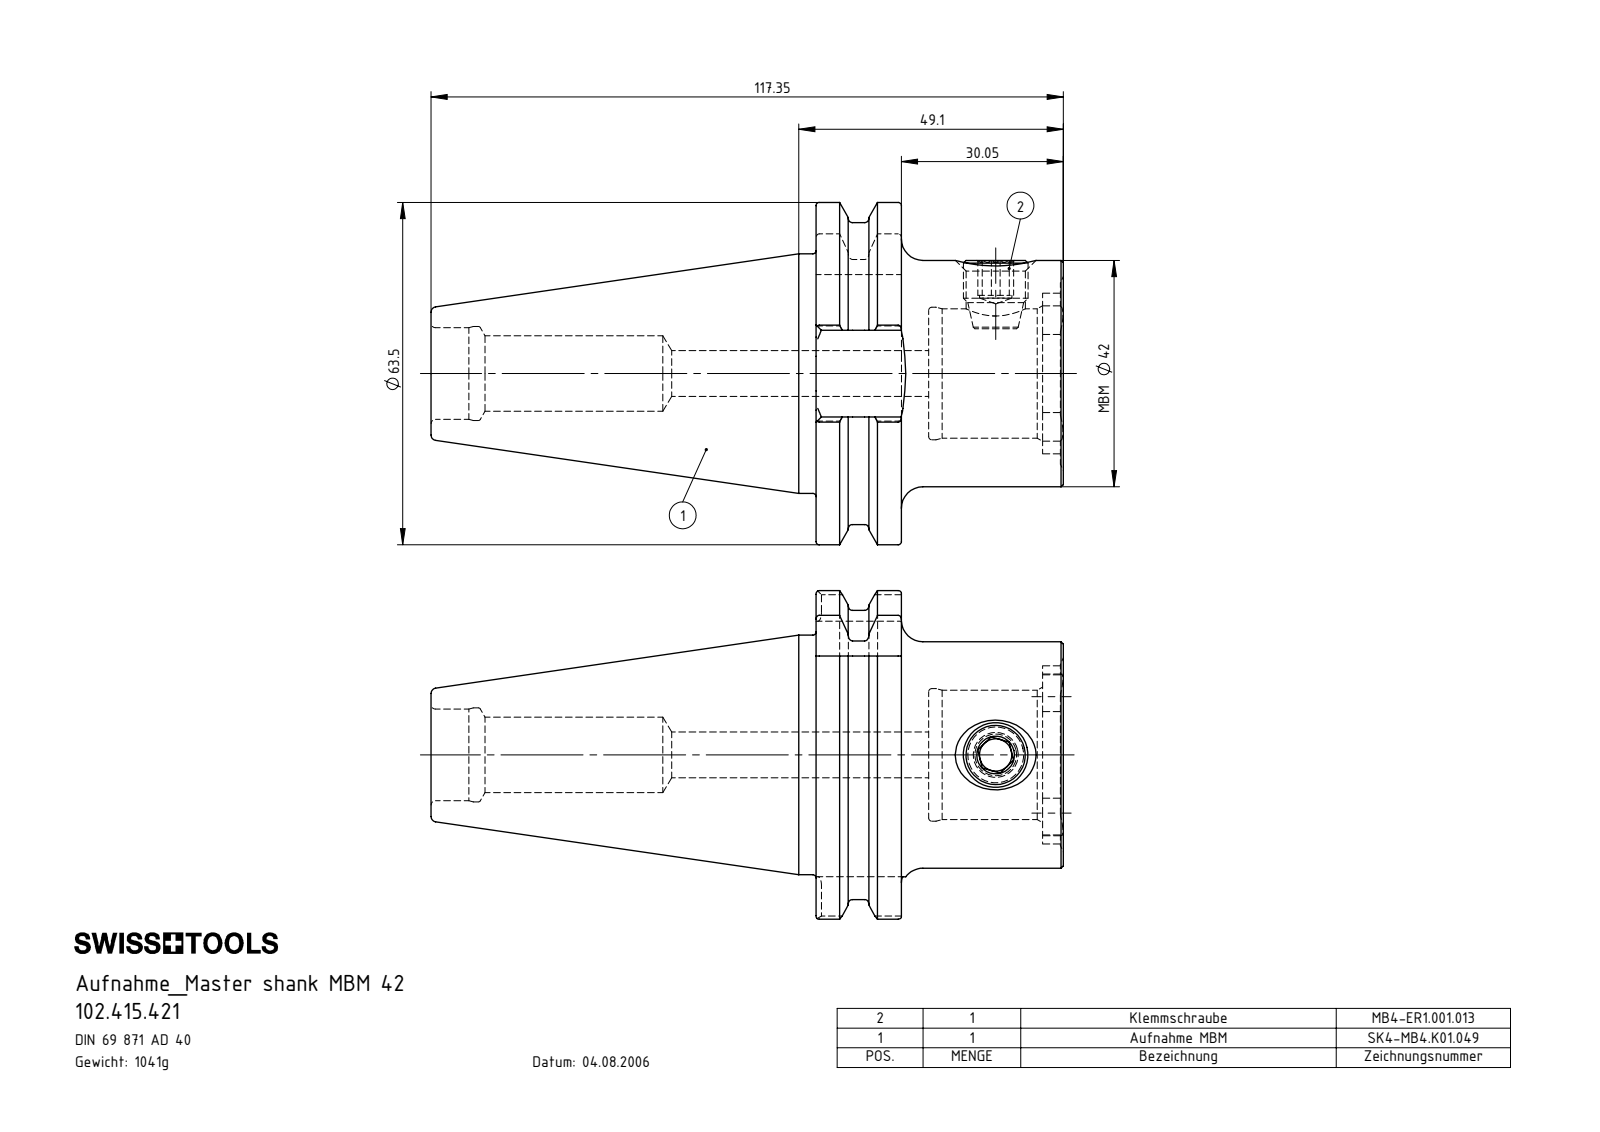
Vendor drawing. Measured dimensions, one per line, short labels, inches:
name: SK4-MB4.K01.049_C; MB4-ER1.001.013_A; 102.415.421
written by: SolidWorks 2017 (CONFIG_CONTROL_DESIGN)
unit: in
bodies: 2 solids, 170 faces (56 planar, 50 cylindrical, 64 other)
size: 4.62 × 2.5 × 2.399
volume: 8.091 in³; area: 40.51 in²
holes: 1× ⌀0.236, 1× ⌀0.335, 1× ⌀0.433, 1× ⌀0.551, 1× ⌀0.669, 1× ⌀0.687, 1× ⌀0.945, 1× ⌀0.969
bosses: 1× ⌀1.75, 1× ⌀1.654, 1× ⌀0.472
rounds: 8× R0.063, 4× R0.165, 1× R0.587, 1× R0.65, 1× R1.102, 1× R1.25
face distances: 0.624, 0.823, 0.199, 1.656, 1.031, 0.833, 0.152, 1.807, 1.183, 0.984
